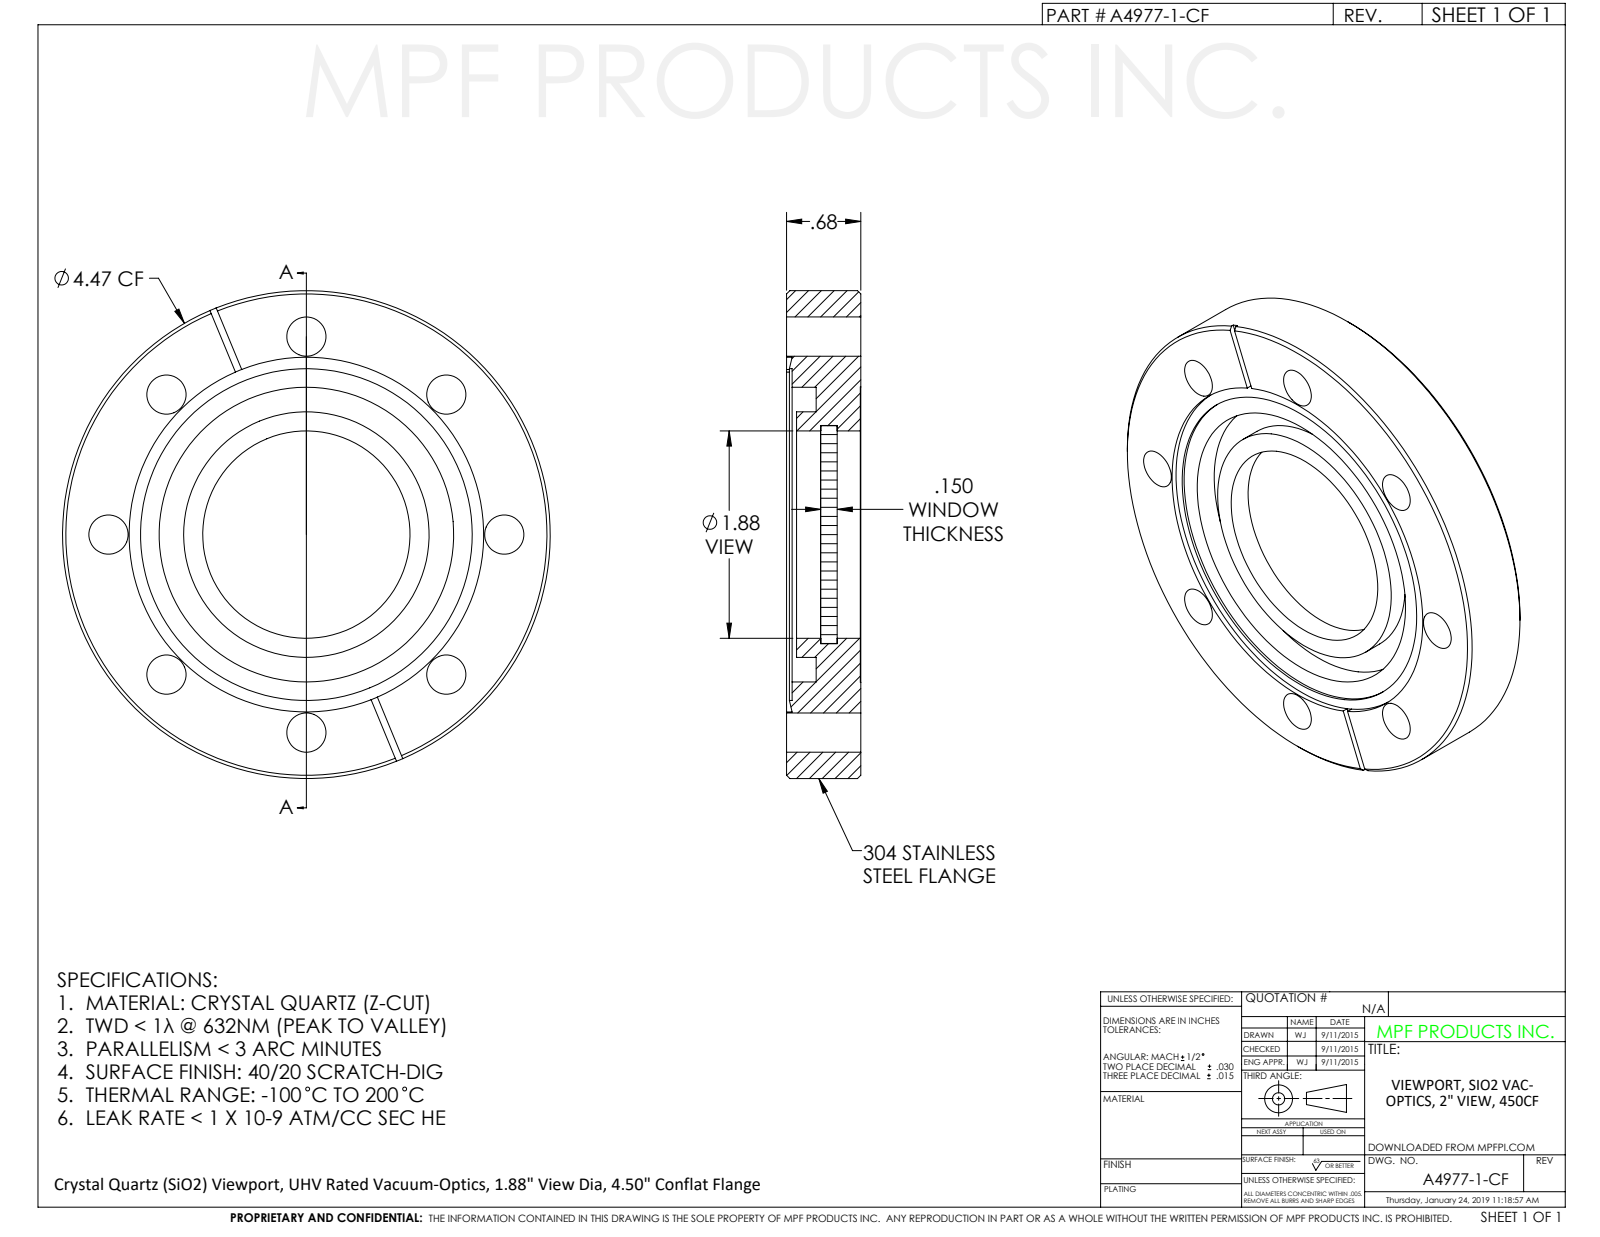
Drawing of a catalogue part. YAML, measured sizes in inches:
part_name: "A4977-1-CF"
step_written_by: "SolidWorks 2020 (CONFIG_CONTROL_DESIGN)"
units: inches
bodies: {solids: 2, faces: 98, planar: 14, cylindrical: 42, other: 42}
overall_size: [4.47, 4.47, 0.68]
volume: 8.011
surface_area: 58.1
round_holes:
  - {diameter: 0.36, count: 8}
  - {diameter: 1.9, count: 1}
  - {diameter: 2, count: 1}
  - {diameter: 2.698, count: 1}
  - {diameter: 3.023, count: 1}
  - {diameter: 3.04, count: 1}
  - {diameter: 3.05, count: 1}
  - {diameter: 3.25, count: 1}
round_bosses_or_shafts:
  - {diameter: 4.47, count: 1}
  - {diameter: 2.823, count: 1}
  - {diameter: 2.25, count: 1}
  - {diameter: 1.996, count: 1}
face_to_face_distances: [0.68, 0.2, 0.671, 0.221, 0.212, 0.459, 0.421, 0.412, 0.259, 0.188]
hole_center_spacings: [1.814, 2.565, 3.352, 1.388, 1.389, 3.628]
